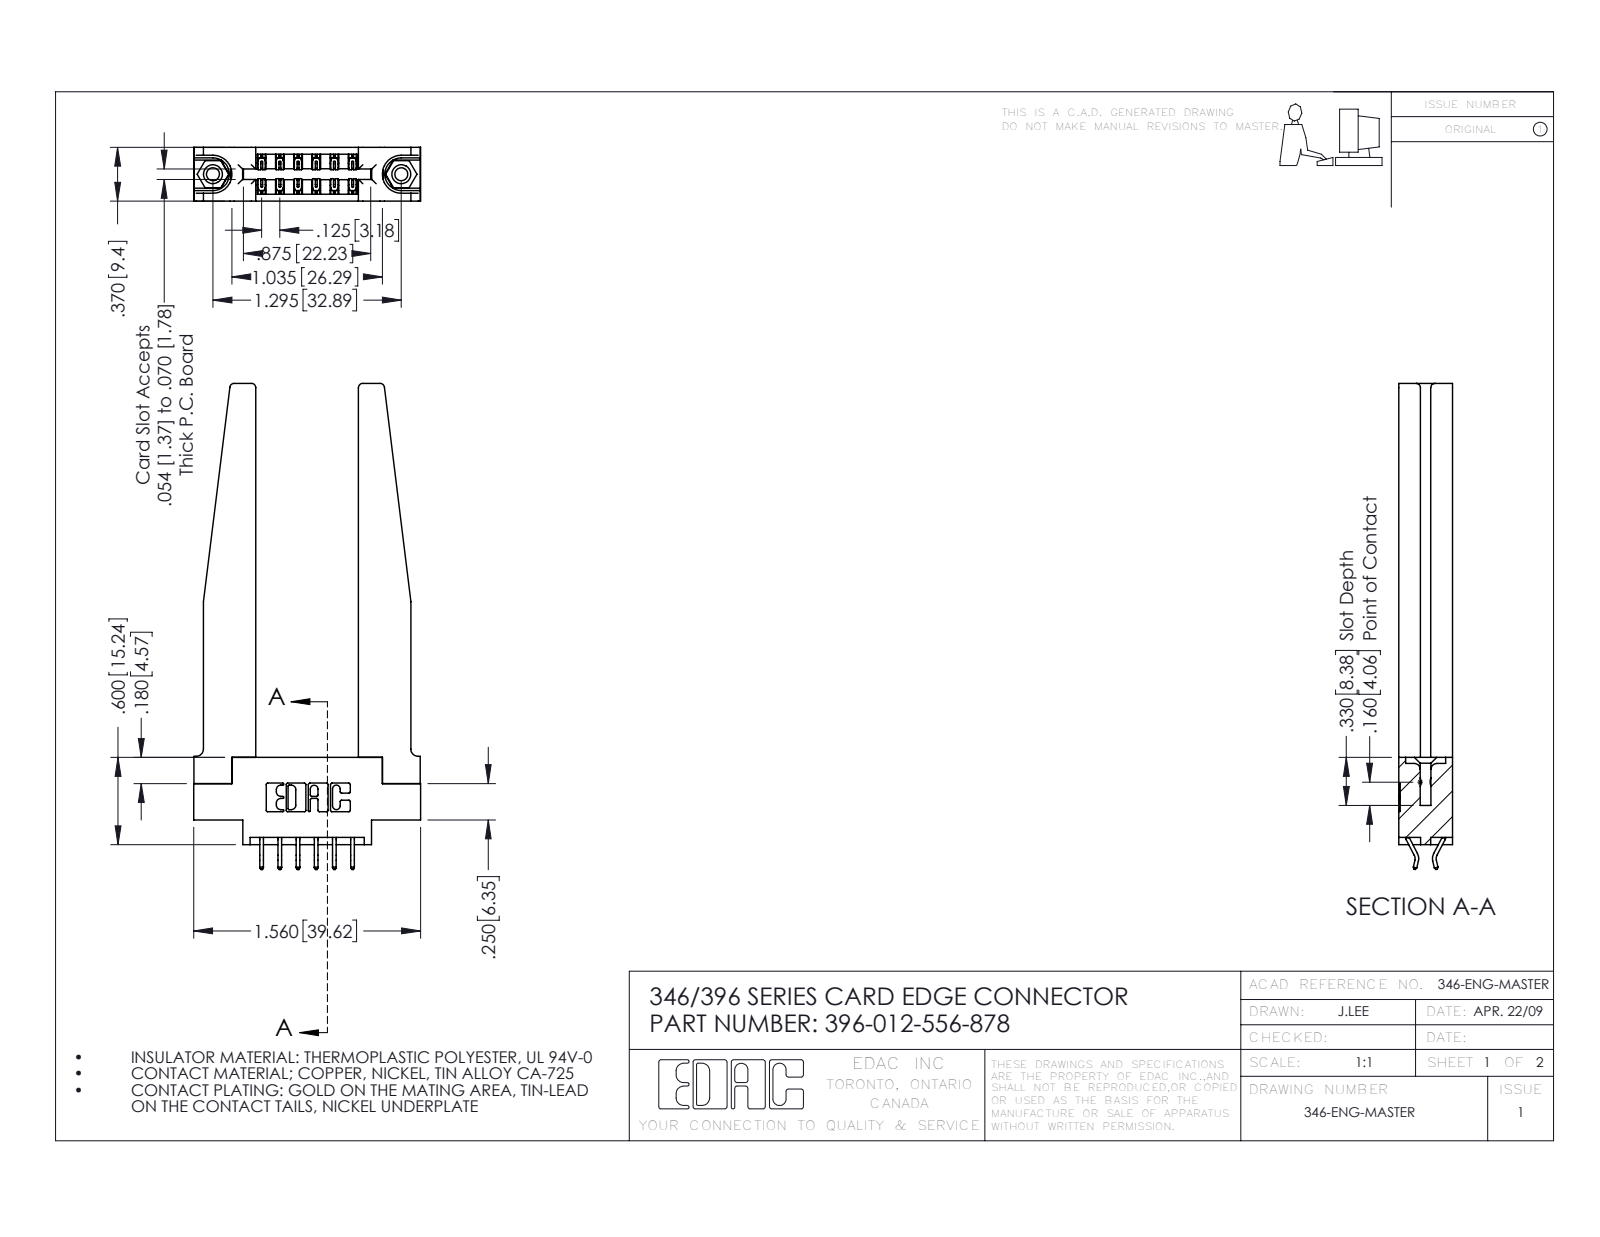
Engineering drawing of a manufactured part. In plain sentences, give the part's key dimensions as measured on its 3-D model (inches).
The part is named "346-220-078_345-220-078; 396-012-556-878; 345-250-001_345-250-001-102; 345-292-001_556 Tail (+1 more)". Its 3-D file was written by "SolidWorks 2016 (CONFIG_CONTROL_DESIGN)". It is 17 solids with 1056 faces: 690 planar, 314 cylindrical and 52 other. Overall it measures 3.34 by 1.56 by 0.37 inches. Its volume is 0.631 cubic inches and its surface area 16.82 square inches. Round holes: 2 of diameter 0.089, 2 of diameter 0.125, 2 of diameter 0.156, 1 of diameter 0.064. Round bosses or shafts: 2 of diameter 0.155. Partial cylindrical surfaces (rounded edges, fillets, slot ends): 22 of radius 0.01, 18 of radius 0.006, 8 of radius 0.03, 6 of radius 0.007, 6 of radius 0.031, 4 of radius 0.05, 3 of radius 0.026, 2 of radius 0.01. The main face-to-face distances are 0.37, 0.15, 0.22, 0.25, 0.706, 0.072, 0.148, 0.102, 0.048, 0.322. The hole center spacings are 0.246, 1.092, 1.295.
